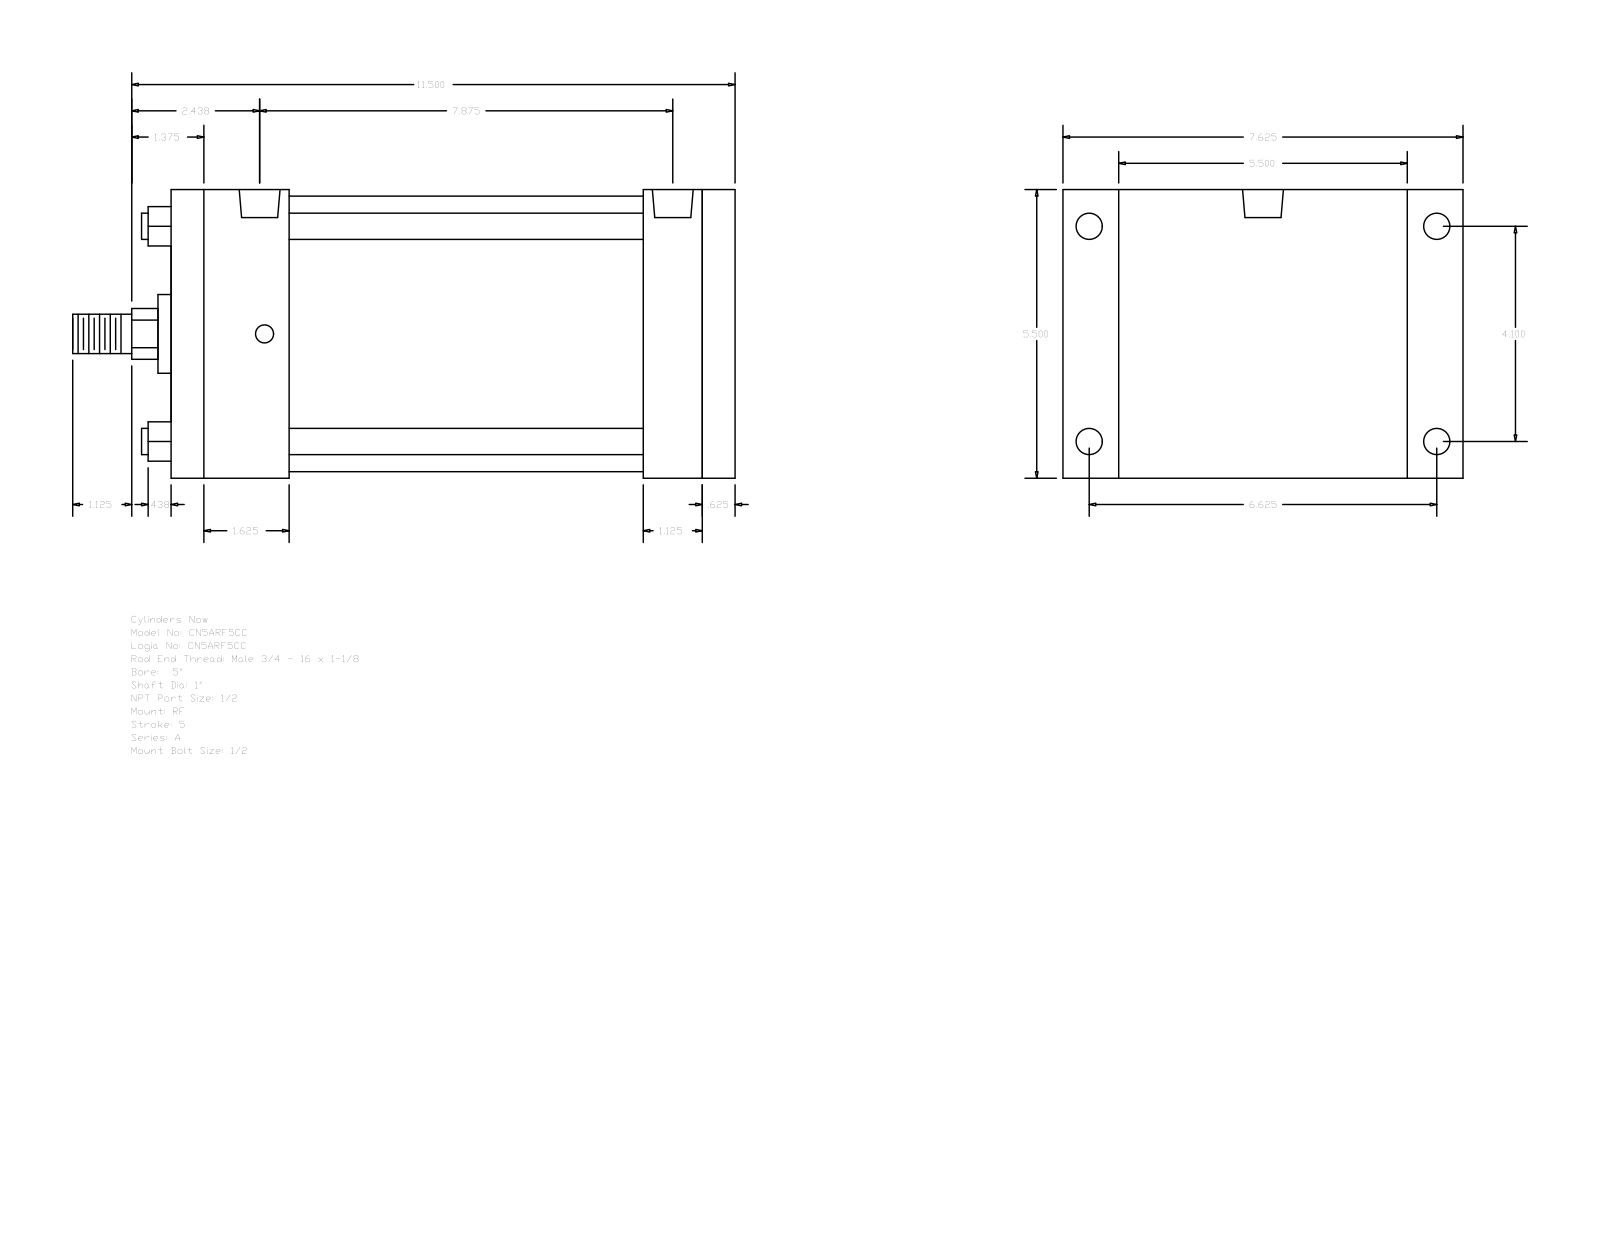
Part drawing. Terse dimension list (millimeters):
name: A_RF__0500_1
written by: GSSL Pune (CONFIG_CONTROL_DESIGN)
unit: mm
bodies: 0 solids, 92 faces (64 planar, 28 cylindrical, 0 other)
size: 320.68 × 193.68 × 139.7
holes: 4× ⌀8.73, 4× ⌀12.7, 2× ⌀19.77
bosses: 4× ⌀12.7, 1× ⌀133.35, 1× ⌀38.1, 1× ⌀25.4, 1× ⌀19.05
rounds: 1× R12.29
face distances: 139.7, 273.05, 257.18, 15.87, 57.15, 200.03, 215.9, 228.6, 171.45, 28.58
hole spacings: 2.39, 104.14, 168.28, 195.25, 197.64, 197.9, 200.03
